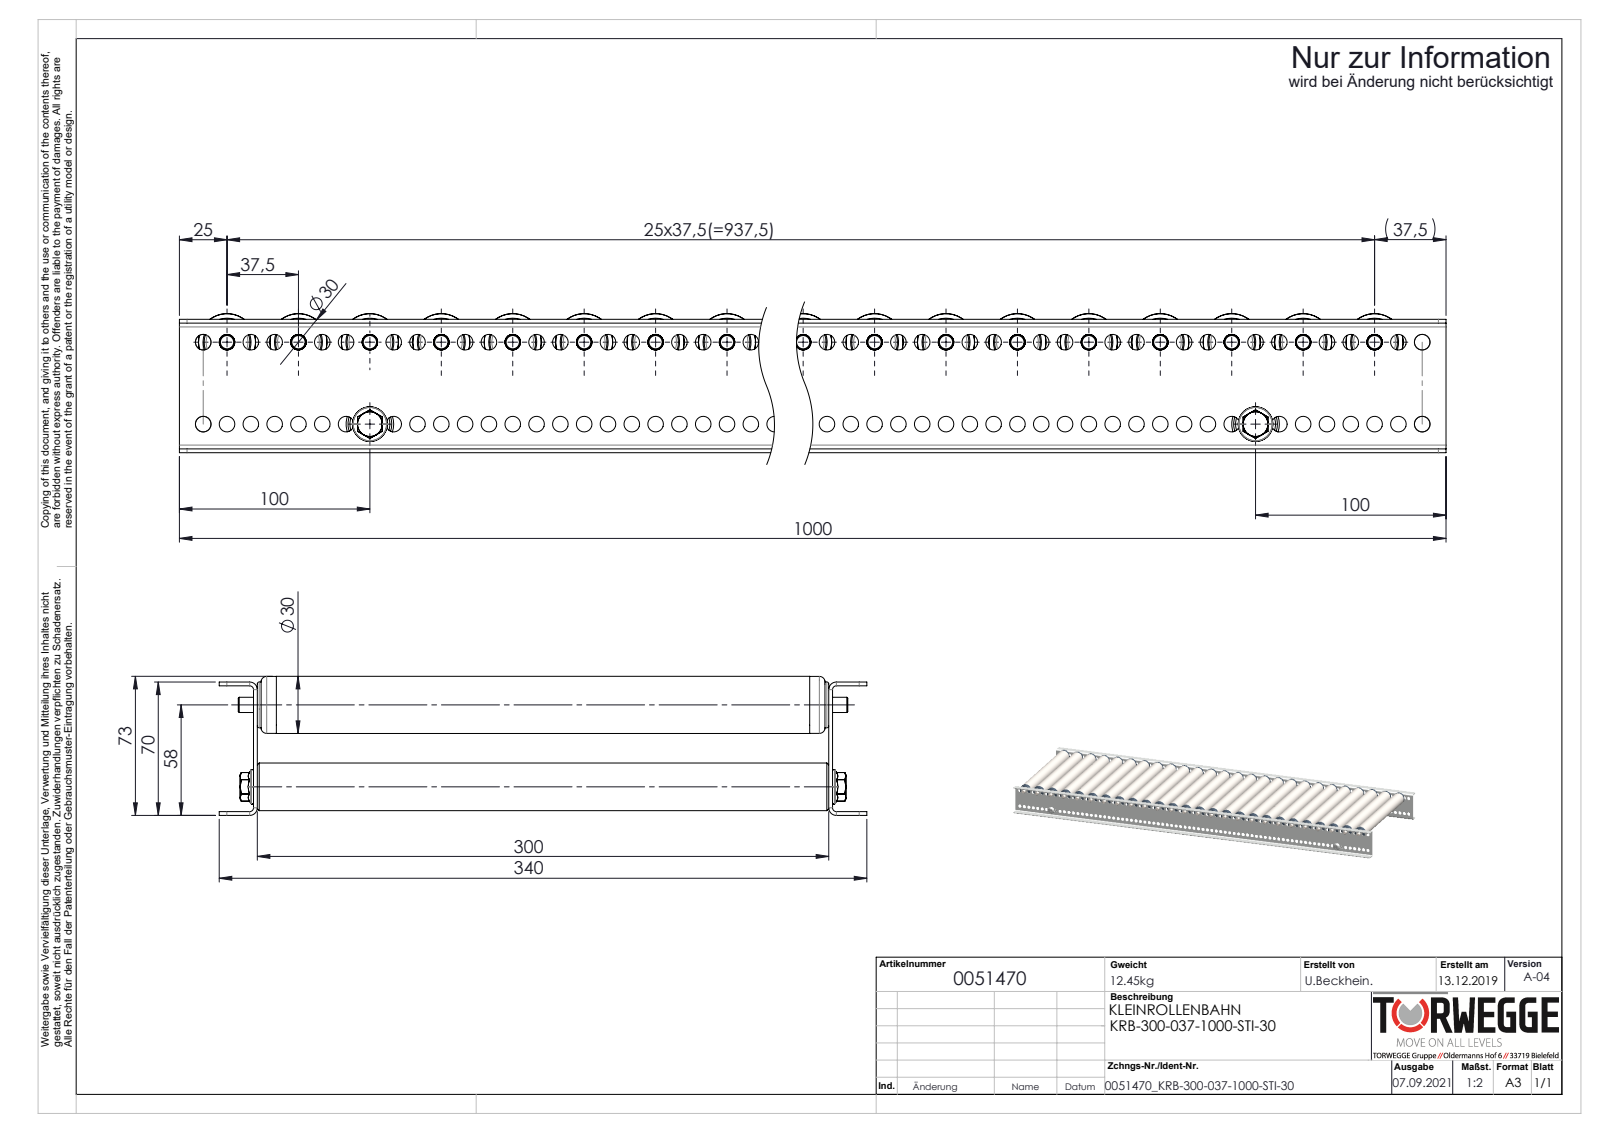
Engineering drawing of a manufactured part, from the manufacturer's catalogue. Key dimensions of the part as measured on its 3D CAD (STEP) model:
Part name (STEP PRODUCT): 0039778-Achse-ST-Ø08-KFG_AL320-G-FA; KUT50-30x1,5-STI-A8-FA_KFG_S100904_KUT50-30x1,5-STI-A8-FA-EL=300; Profil_KRB-20x70x20x2_KFG_S100230_U-PROFIL-20-70-20-2-KRB-30-L=1000; Traversen_KFG_L300 (+6 more)
STEP written by: SolidWorks 2020 (AUTOMOTIVE_DESIGN)
Units: millimetres
Bodies: 168 solids, 6996 faces (2200 planar, 2768 cylindrical, 2028 other)
Overall size (bounding box): 1000 × 340 × 73
Volume: 1 906 000 mm³ · Surface area: 2 392 000 mm²
Round holes (diameter × count): ⌀8.2 ×158, ⌀8 ×26, ⌀8.1 ×26, ⌀23.2 ×26, ⌀25.2 ×26, ⌀27 ×26, ⌀6.8 ×2, ⌀21 ×2
Round bosses / shafts (diameter × count): ⌀30 ×26, ⌀29.9 ×26, ⌀27.1 ×26, ⌀26.8 ×26, ⌀24 ×26, ⌀14 ×26, ⌀25 ×2, ⌀8 ×2
Partial cylindrical surfaces — rounded edges, fillets, slot ends (radius × count): R5.05 ×26, R4 ×8, R2 ×4
Main face-to-face distances: 2, 302, 300, 68, 304, 66, 70, 10, 290, 20
Hole centre spacings: 12.5, 25, 37.5, 50, 62.5, 75, 87.5, 100
